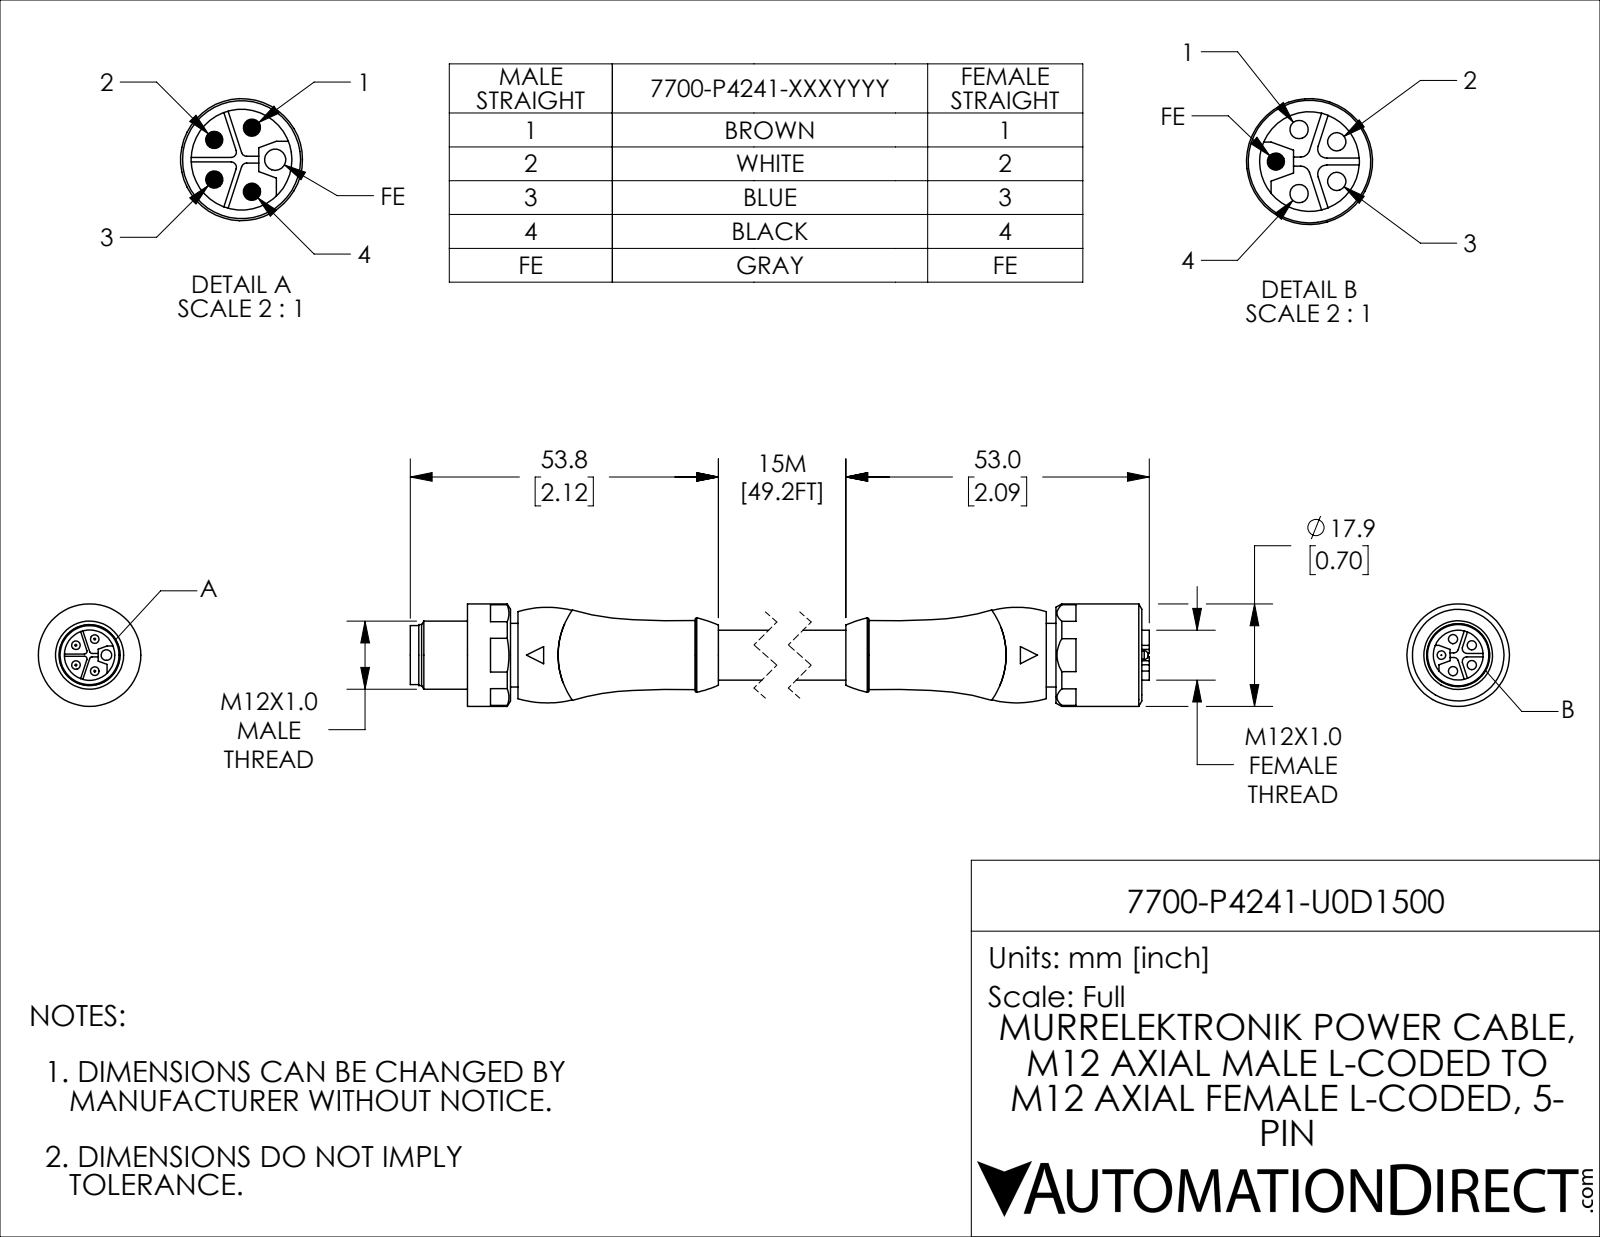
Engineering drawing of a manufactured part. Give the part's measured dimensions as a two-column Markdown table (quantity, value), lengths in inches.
| quantity | value |
| --- | --- |
| part name | 7700-P4241-U0D1500_2; 7700-P4241-U0D1500_1; 7700-P4241-U0D1500 |
| STEP written by | SolidWorks 2021 (CONFIG_CONTROL_DESIGN) |
| units | inches |
| bodies | 3 solids, 214 faces (98 planar, 62 cylindrical, 54 other) |
| overall size | 5.386 × 0.705 × 0.705 |
| volume | 1.09 in³ |
| surface area | 14.44 in² |
| round holes (diameter × count) | 0.063 × 4, 0.073 × 1, 0.346 × 1, 0.433 × 1, 0.512 × 1 |
| round bosses / shafts (diameter × count) | 0.059 × 5, 0.705 × 1, 0.51 × 1, 0.469 × 1, 0.437 × 1, 0.419 × 1, 0.406 × 1, 0.343 × 1 |
| partial cylindrical surfaces (radius × count) | 0.018 × 4, 0.031 × 4 |
| main face-to-face distances | 4.283, 0.067, 0.346, 0.666, 0.051, 0.295, 0.228, 4.941, 0.657, 4.35 |
| hole center spacings | 0.116, 0.136, 0.22, 0.22 |
